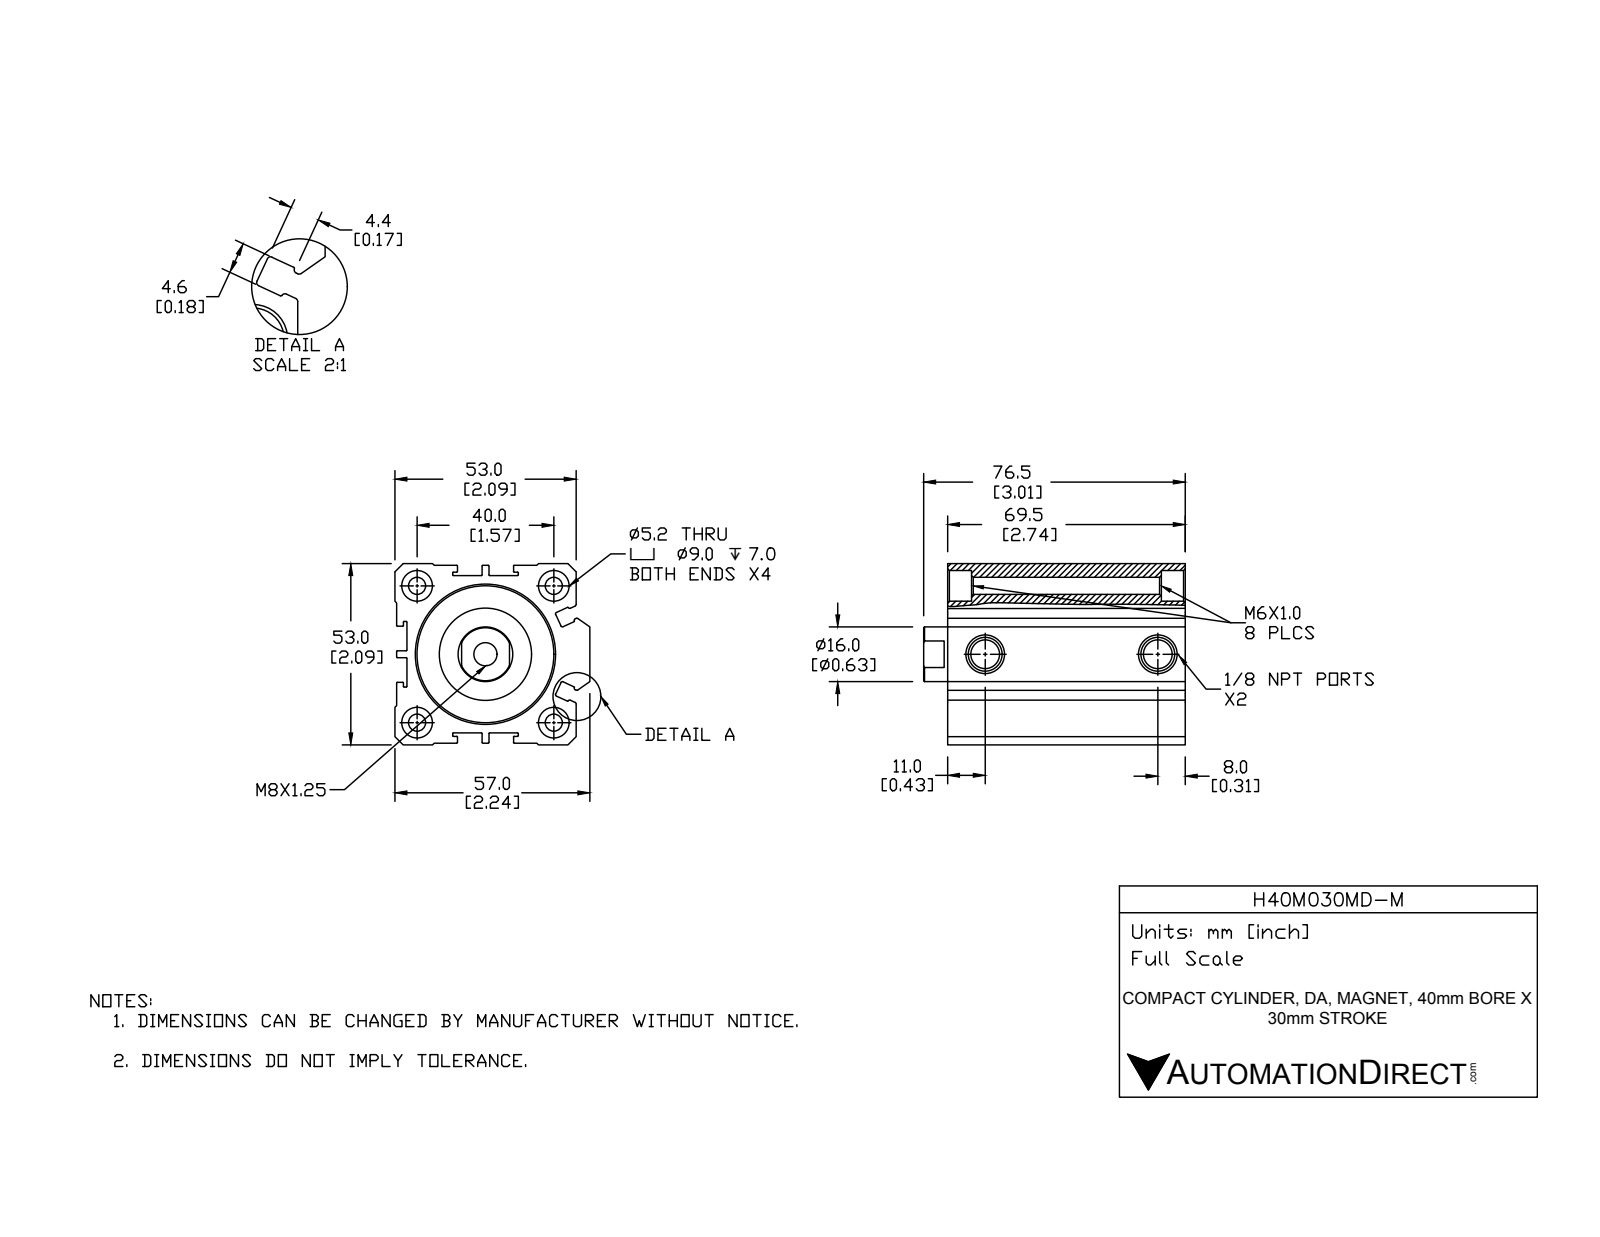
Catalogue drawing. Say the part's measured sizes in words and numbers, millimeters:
The part is named "H40M030MD-M-PISTON; H40M030MD-M-BODY; H40M030MD-M". Its 3-D file was written by "SolidWorks 2015 (CONFIG_CONTROL_DESIGN)". It is 2 solids with 255 faces: 99 planar, 103 cylindrical and 53 other. Overall it measures 76.5 by 57 by 53 millimeters. Its volume is 136 640 cubic millimeters and its surface area 48 736 square millimeters. Round holes: 4 of diameter 5, 4 of diameter 9, 2 of diameter 8.43, 1 of diameter 6.8, 1 of diameter 16, 1 of diameter 29.5, 1 of diameter 40. Round bosses or shafts: 1 of diameter 27, 1 of diameter 25. Partial cylindrical surfaces (rounded edges, fillets, slot ends): 40 of radius 0.2, 12 of radius 0.5. The main face-to-face distances are 3.5, 49.5, 52.5, 0.5, 3, 53, 49, 69.5, 25, 46. The hole center spacings are 28.28, 40, 56.57, 50.5.
